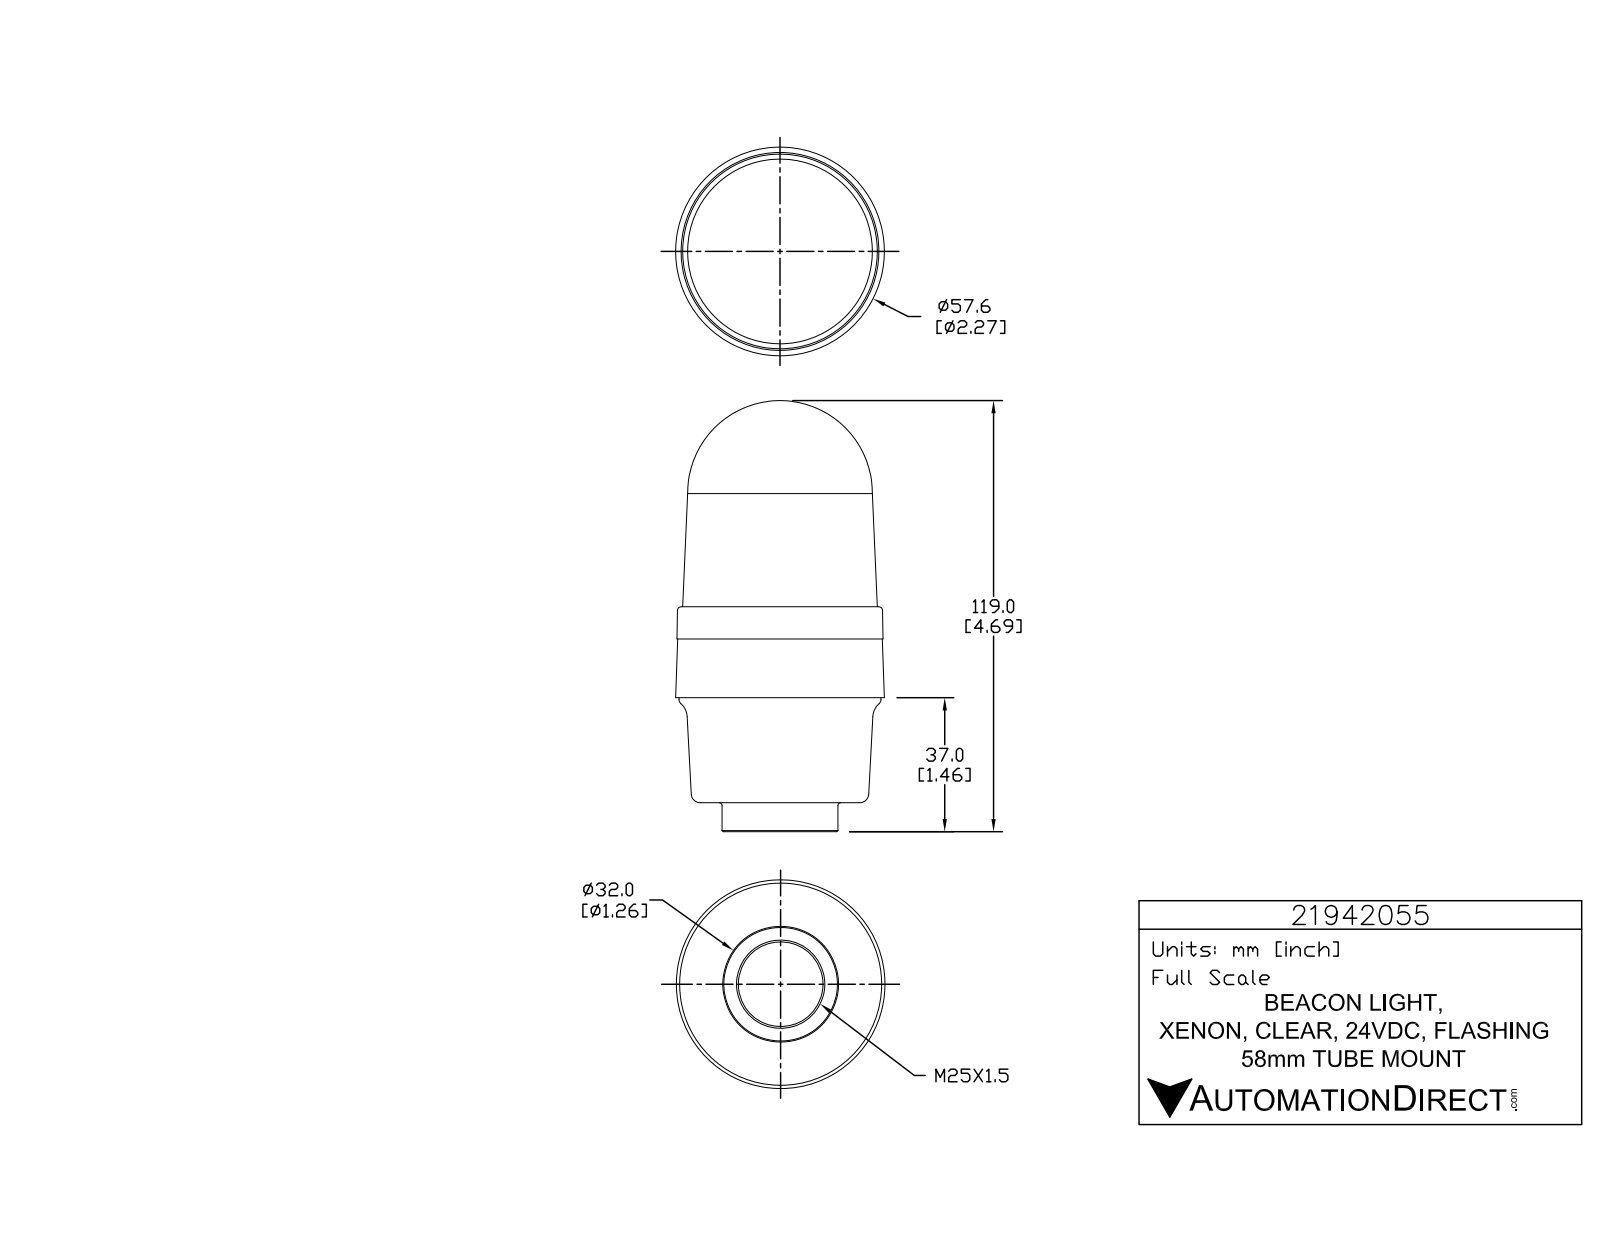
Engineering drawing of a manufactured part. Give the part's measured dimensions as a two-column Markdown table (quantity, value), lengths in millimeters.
| quantity | value |
| --- | --- |
| part name | 21942055 |
| STEP written by | SolidWorks 2015 (AUTOMOTIVE_DESIGN) |
| units | millimeters |
| bodies | 1 solid, 791 faces (525 planar, 168 cylindrical, 98 other) |
| overall size | 119 × 57.6 × 57.6 |
| volume | 227 600 mm³ |
| surface area | 21 970 mm² |
| round holes (diameter × count) | 1 × 3, 23.4 × 1 |
| round bosses / shafts (diameter × count) | 5.7 × 3, 1.4 × 3, 55.8 × 1, 32 × 1 |
| partial cylindrical surfaces (radius × count) | 0.2 × 6, 0.2 × 6, 0.2 × 6, 3.3 × 6, 0.1 × 3, 0.1 × 3, 0.2 × 3, 0.2 × 3 |
| main face-to-face distances | 8, 29, 37, 25.1, 54.1, 62.1, 8.9, 16.2, 45.2, 53.2 |
